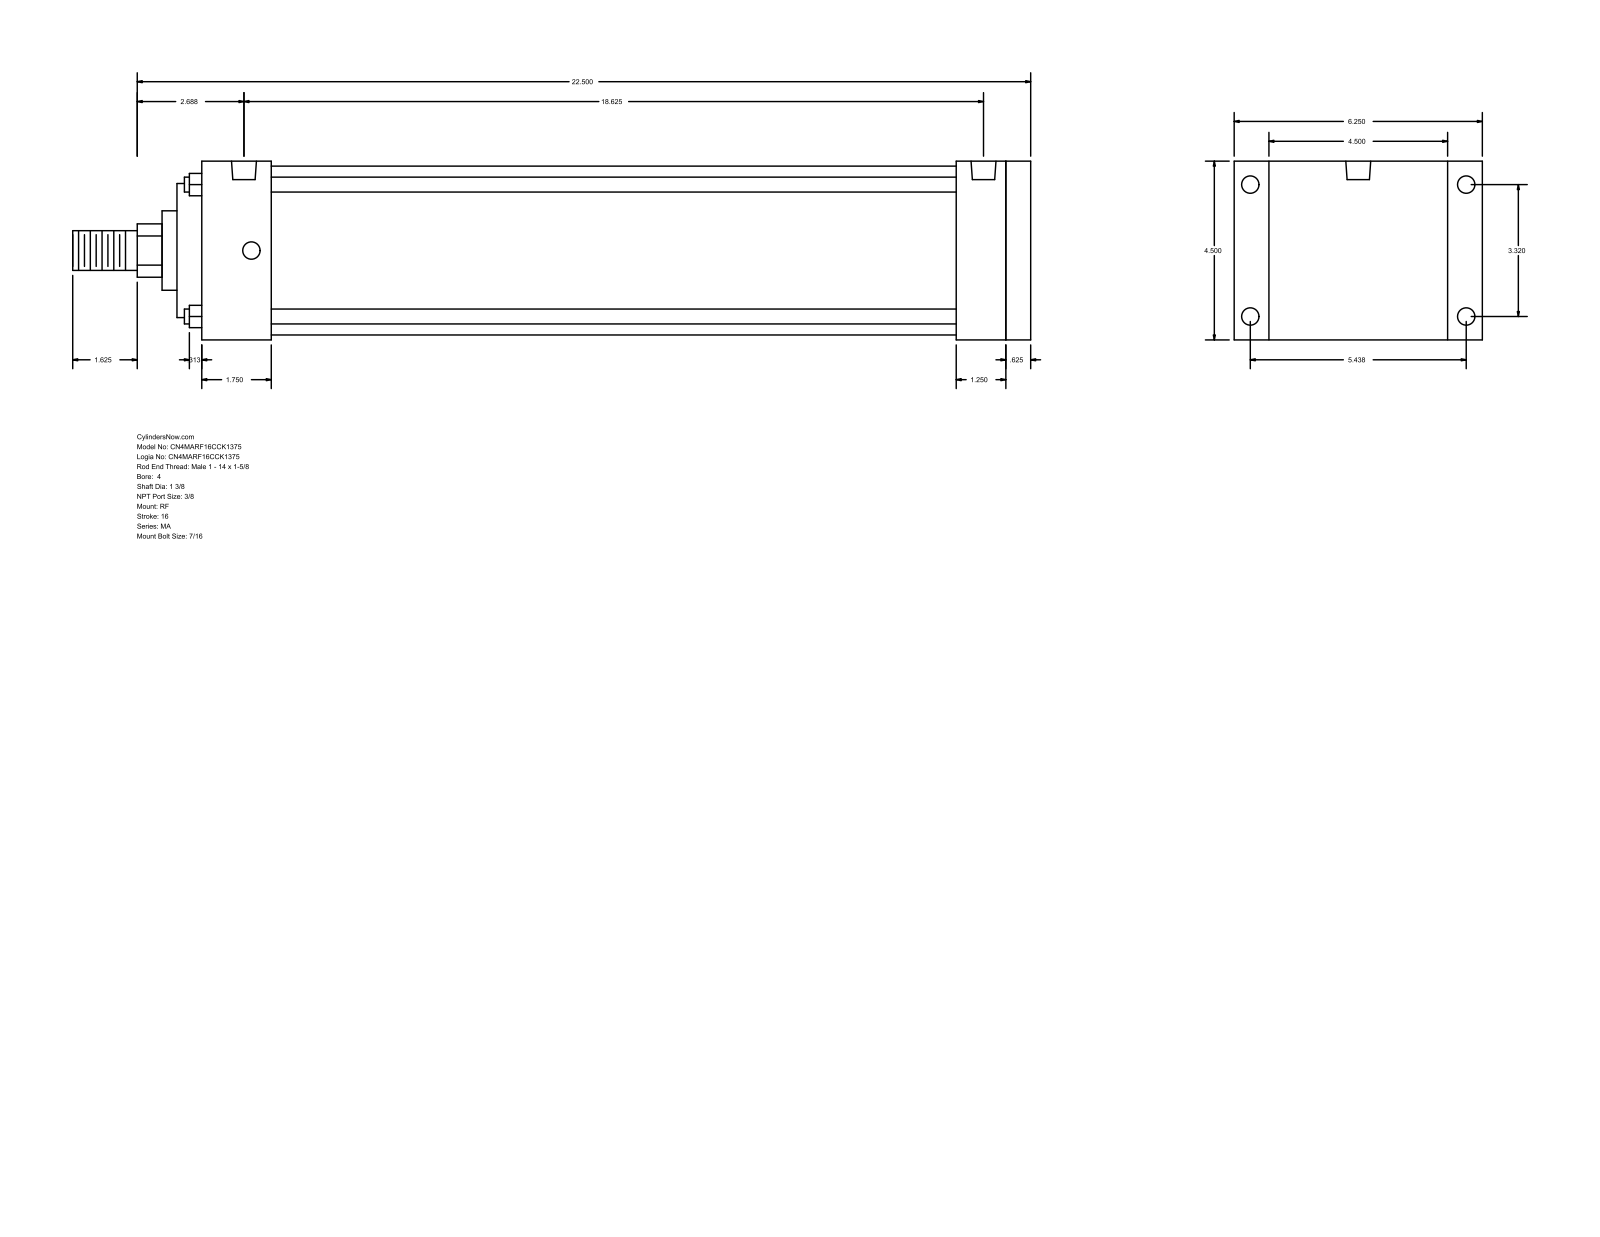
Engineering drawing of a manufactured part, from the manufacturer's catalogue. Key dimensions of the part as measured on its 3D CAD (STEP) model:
Part name (STEP PRODUCT): MA_RF__0400_1.375
STEP written by: GSSL Pune (CONFIG_CONTROL_DESIGN)
Units: millimetres
Bodies: 0 solids, 94 faces (65 planar, 29 cylindrical, 0 other)
Overall size (bounding box): 612.77 × 158.75 × 114.3
Round holes (diameter × count): ⌀11.11 ×8, ⌀15.93 ×2
Round bosses / shafts (diameter × count): ⌀9.53 ×4, ⌀107.95 ×1, ⌀85.72 ×1, ⌀50.8 ×1, ⌀34.92 ×1, ⌀25.4 ×1
Partial cylindrical surfaces — rounded edges, fillets, slot ends (radius × count): R17.06 ×1
Main face-to-face distances: 114.3, 530.23, 15.88, 514.35, 15.87, 530.22, 546.1, 22.23, 136.53, 498.48
Hole centre spacings: 84.32, 138.12, 161.82, 463.55, 4.76, 4.77, 468.31, 468.32
